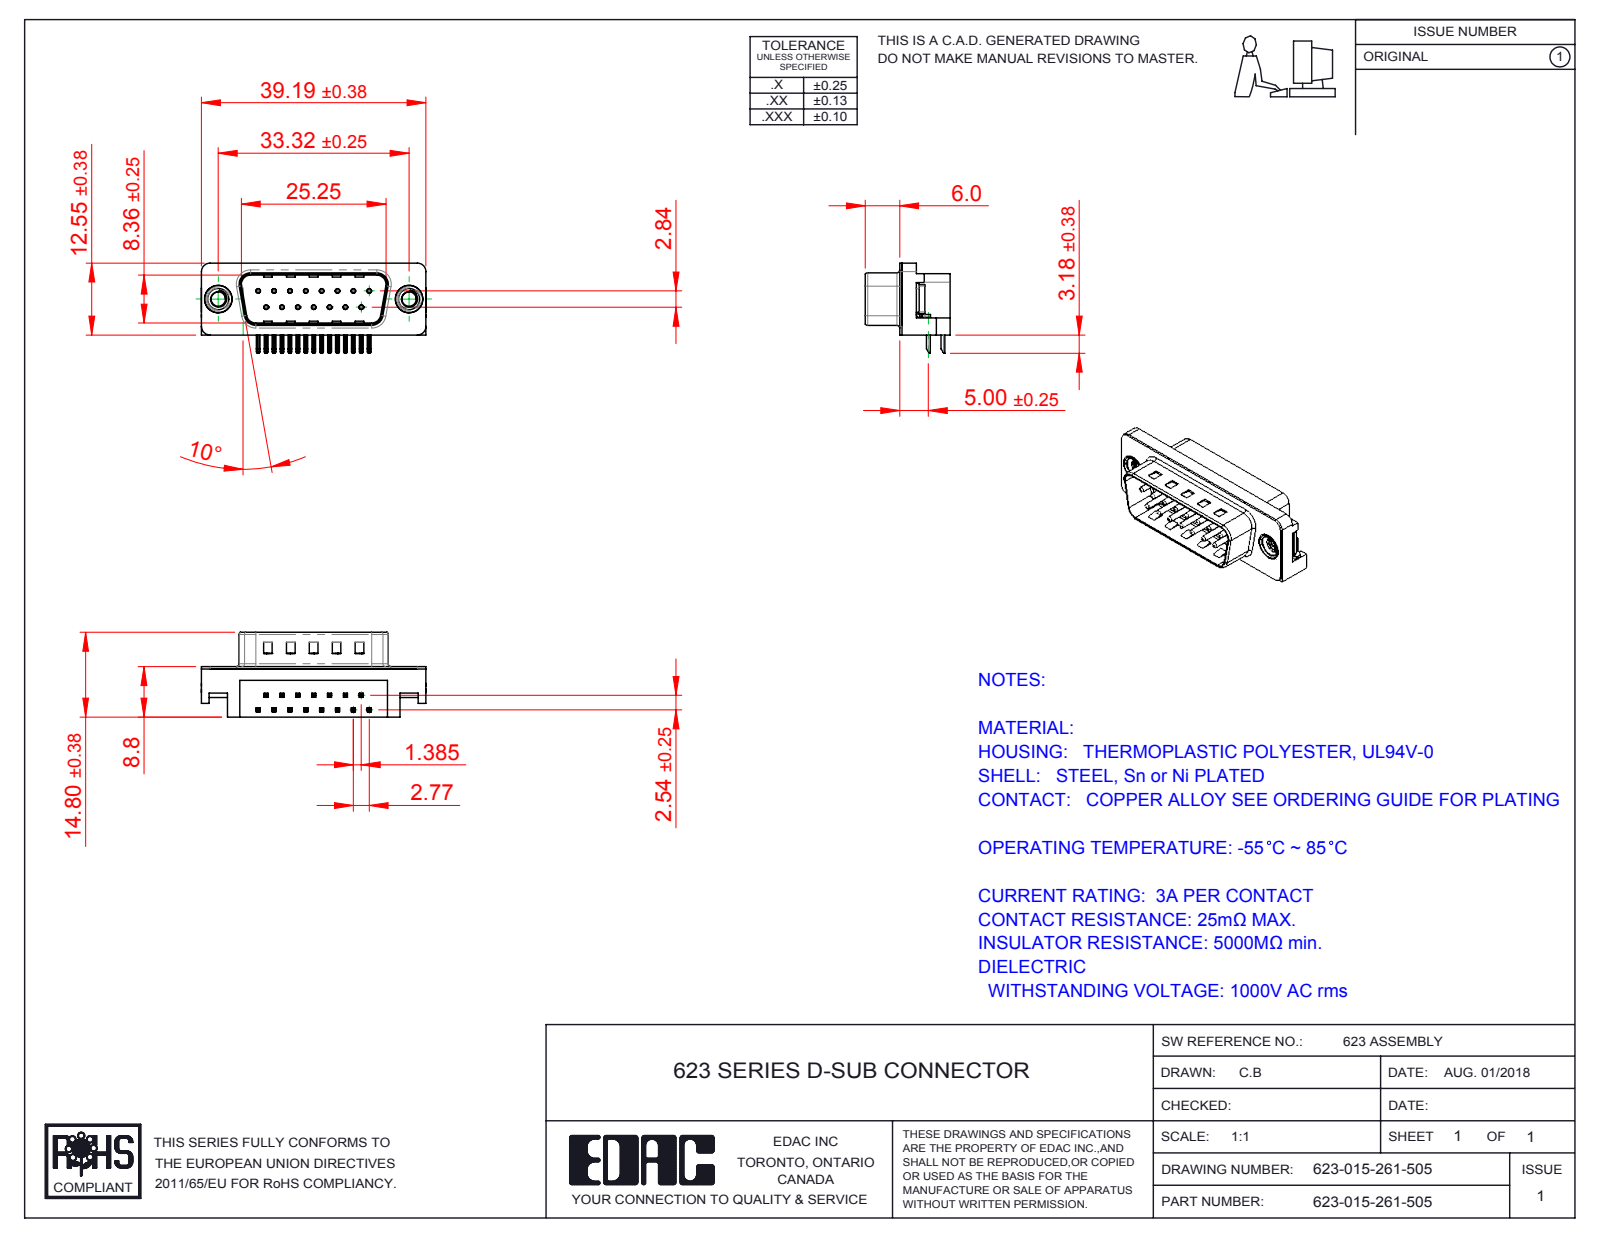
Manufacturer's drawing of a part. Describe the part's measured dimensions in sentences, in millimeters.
The part is named "623 Non Board Mount; 623 M3 Threaded Rivet; 623-015-261-505; 623 Contact Bottom (+3 more)". Its 3-D file was written by "SolidWorks 2016 (CONFIG_CONTROL_DESIGN)". It is 21 solids with 1467 faces: 893 planar, 439 cylindrical and 135 other. Overall it measures 39.22 by 15.73 by 14.8 millimeters. Its volume is 3 313 cubic millimeters and its surface area 4 888 square millimeters. Round holes: 15 of diameter 0.35, 15 of diameter 0.8, 2 of diameter 2.5, 2 of diameter 4, 2 of diameter 4.8, 2 of diameter 5. Round bosses or shafts: 15 of diameter 0.75, 2 of diameter 4.9, 2 of diameter 4.75, 2 of diameter 3.9. Partial cylindrical surfaces (rounded edges, fillets, slot ends): 68 of radius 0.25, 30 of radius 0.12, 16 of radius 1, 9 of radius 0.5, 6 of radius 1.5, 4 of radius 0.9, 4 of radius 1.6, 4 of radius 2. The main face-to-face distances are 0.4, 8.4, 2.1, 1.7, 10.46, 8.8, 10.86, 8.76, 5.9, 2.9. The hole center spacings are 3.16, 2.77, 5.54, 8.31, 11.08, 5.03, 5.04, 7.48.
